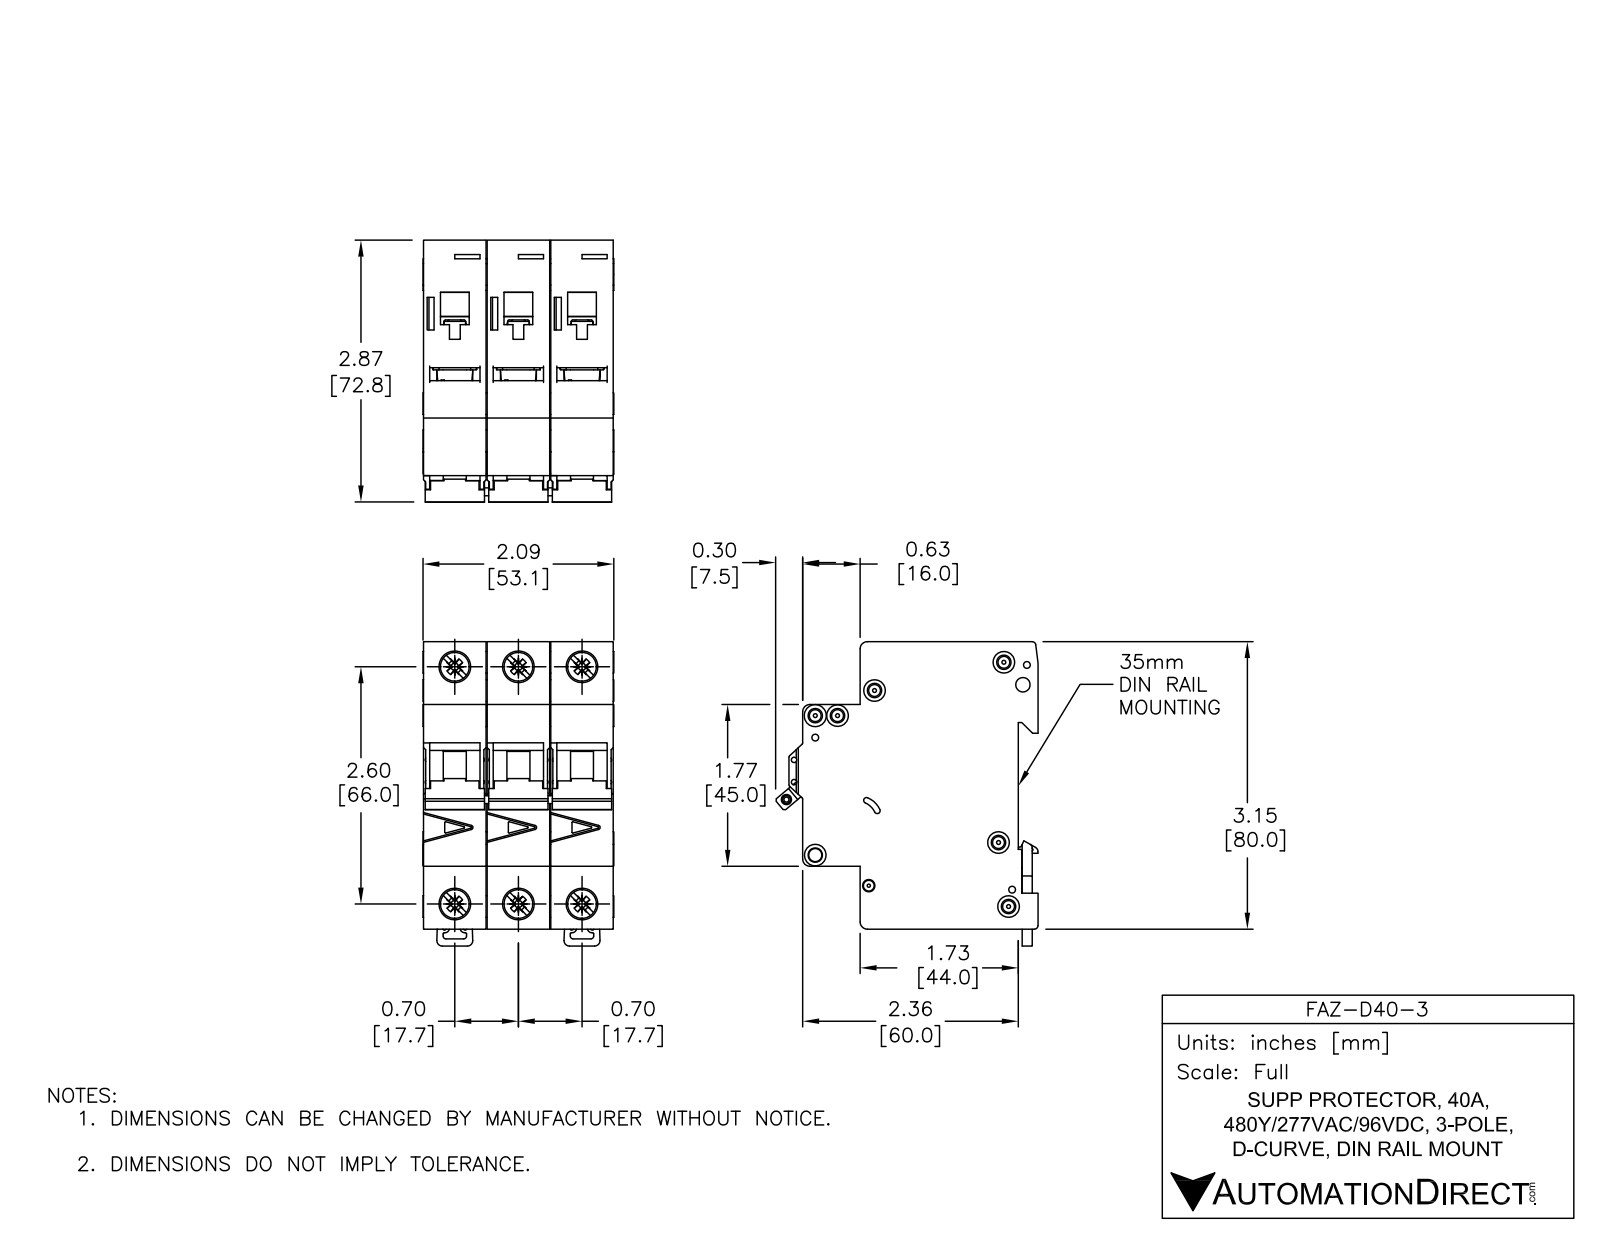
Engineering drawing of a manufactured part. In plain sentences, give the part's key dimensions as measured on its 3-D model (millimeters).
The part is named "FAZ-D40-3". Its 3-D file was written by "SolidWorks 2014 (AUTOMOTIVE_DESIGN)". It is 11 solids with 1650 faces: 697 planar, 590 cylindrical and 363 other. Overall it measures 84.78 by 73.04 by 53.1 millimeters. Its volume is 224 680 cubic millimeters and its surface area 58 052 square millimeters. Round holes: 6 of diameter 3.6, 4 of diameter 8.2, 3 of diameter 1.9, 2 of diameter 1.09, 2 of diameter 1.5, 2 of diameter 4, 2 of diameter 7.15, 1 of diameter 2.15, 1 of diameter 2.2, 1 of diameter 2.55, 1 of diameter 3.3, 1 of diameter 3.4. Round bosses or shafts: 4 of diameter 6, 3 of diameter 2.5, 2 of diameter 8.2. Partial cylindrical surfaces (rounded edges, fillets, slot ends): 68 of radius 0.25, 25 of radius 0.5, 12 of radius 1, 12 of radius 2, 11 of radius 0.2, 3 of radius 1.8, 2 of radius 0.8, 2 of radius 3. The main face-to-face distances are 17.7, 17.5, 35.4, 35.2, 52.9, 17.9, 79.48, 5.5, 49.5, 44. The hole center spacings are 17.7, 68.33, 66, 6.2, 13.64, 35.4, 74.89, 4.81.
